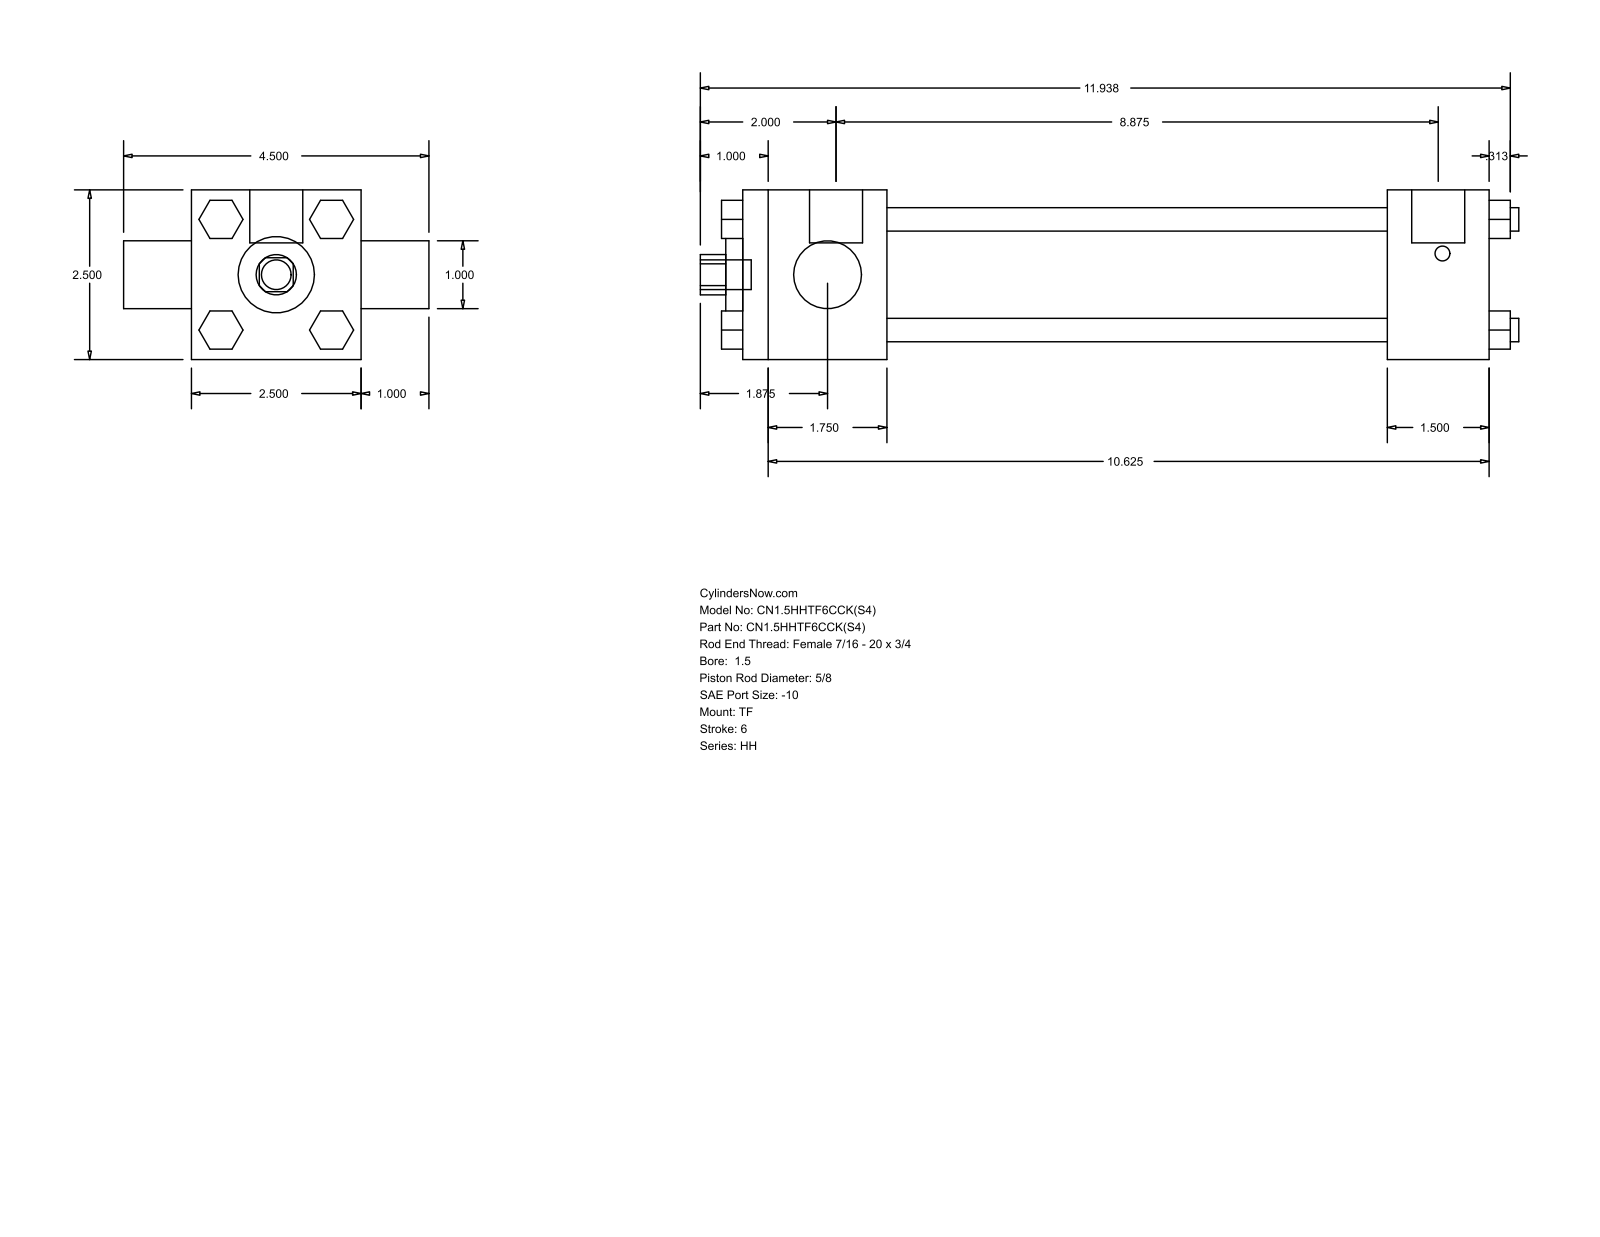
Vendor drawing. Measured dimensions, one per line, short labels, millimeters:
name: HH_TF__0150_0.625
written by: GSSL Pune (CONFIG_CONTROL_DESIGN)
unit: mm
bodies: 0 solids, 120 faces (92 planar, 28 cylindrical, 0 other)
size: 306.39 × 114.3 × 63.5
holes: 1× ⌀15.88, 1× ⌀25.4, 1× ⌀28.57, 1× ⌀44.45
bosses: 4× ⌀8.76, 3× ⌀5.56, 2× ⌀19.84, 1× ⌀11.11
rounds: 1× R7.54
face distances: 63.5, 279.39, 53.97, 225.42, 241.3, 187.33, 38.09, 25.4, 20.7, 14.29
